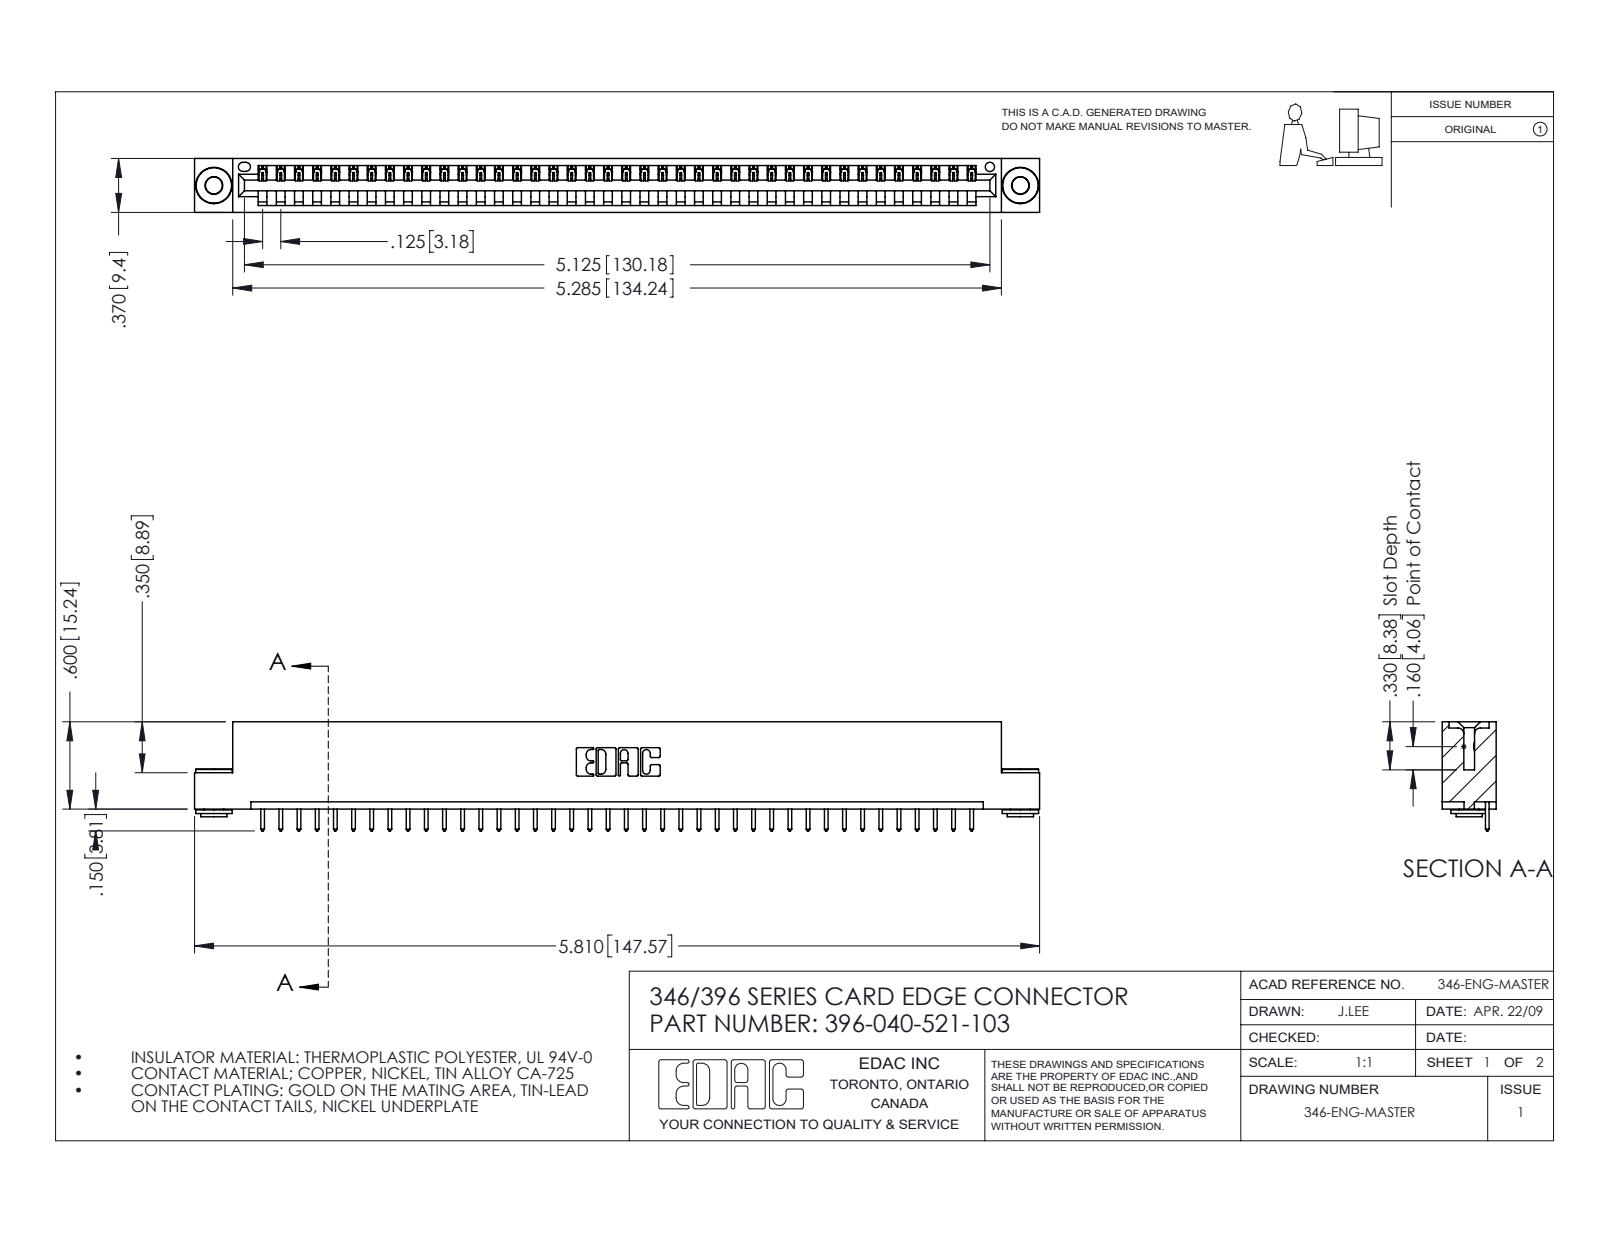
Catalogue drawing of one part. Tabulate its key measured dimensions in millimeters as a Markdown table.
| quantity | value |
| --- | --- |
| part name | 346 Part_Flush Mounting Lugs - 0.156 Dia-TH; 345-292-001_345-293-121; 396-040-521-103; 345-250-002_345-250-002-102 |
| STEP written by | SolidWorks 2016 (CONFIG_CONTROL_DESIGN) |
| units | millimeters |
| bodies | 43 solids, 2480 faces (1686 planar, 786 cylindrical, 8 other) |
| overall size | 147.6 × 19.1 × 9.4 |
| volume | 14 000 mm³ |
| surface area | 17 260 mm² |
| round holes (diameter × count) | 2.9 × 2, 4 × 2, 1.6 × 1 |
| round bosses / shafts (diameter × count) | 6.4 × 2, 4.6 × 2, 3.5 × 2 |
| partial cylindrical surfaces (radius × count) | 0.2 × 80, 0.3 × 80, 0.3 × 22, 0.2 × 6, 0.8 × 6, 0.7 × 3, 0.8 × 2, 1 × 2 |
| main face-to-face distances | 1.2, 8.2, 9.4, 6.4, 0.6, 1.8, 7.6, 3.8, 5.6, 2.5 |
| hole center spacings | 6.2, 135.5, 140.8 |
